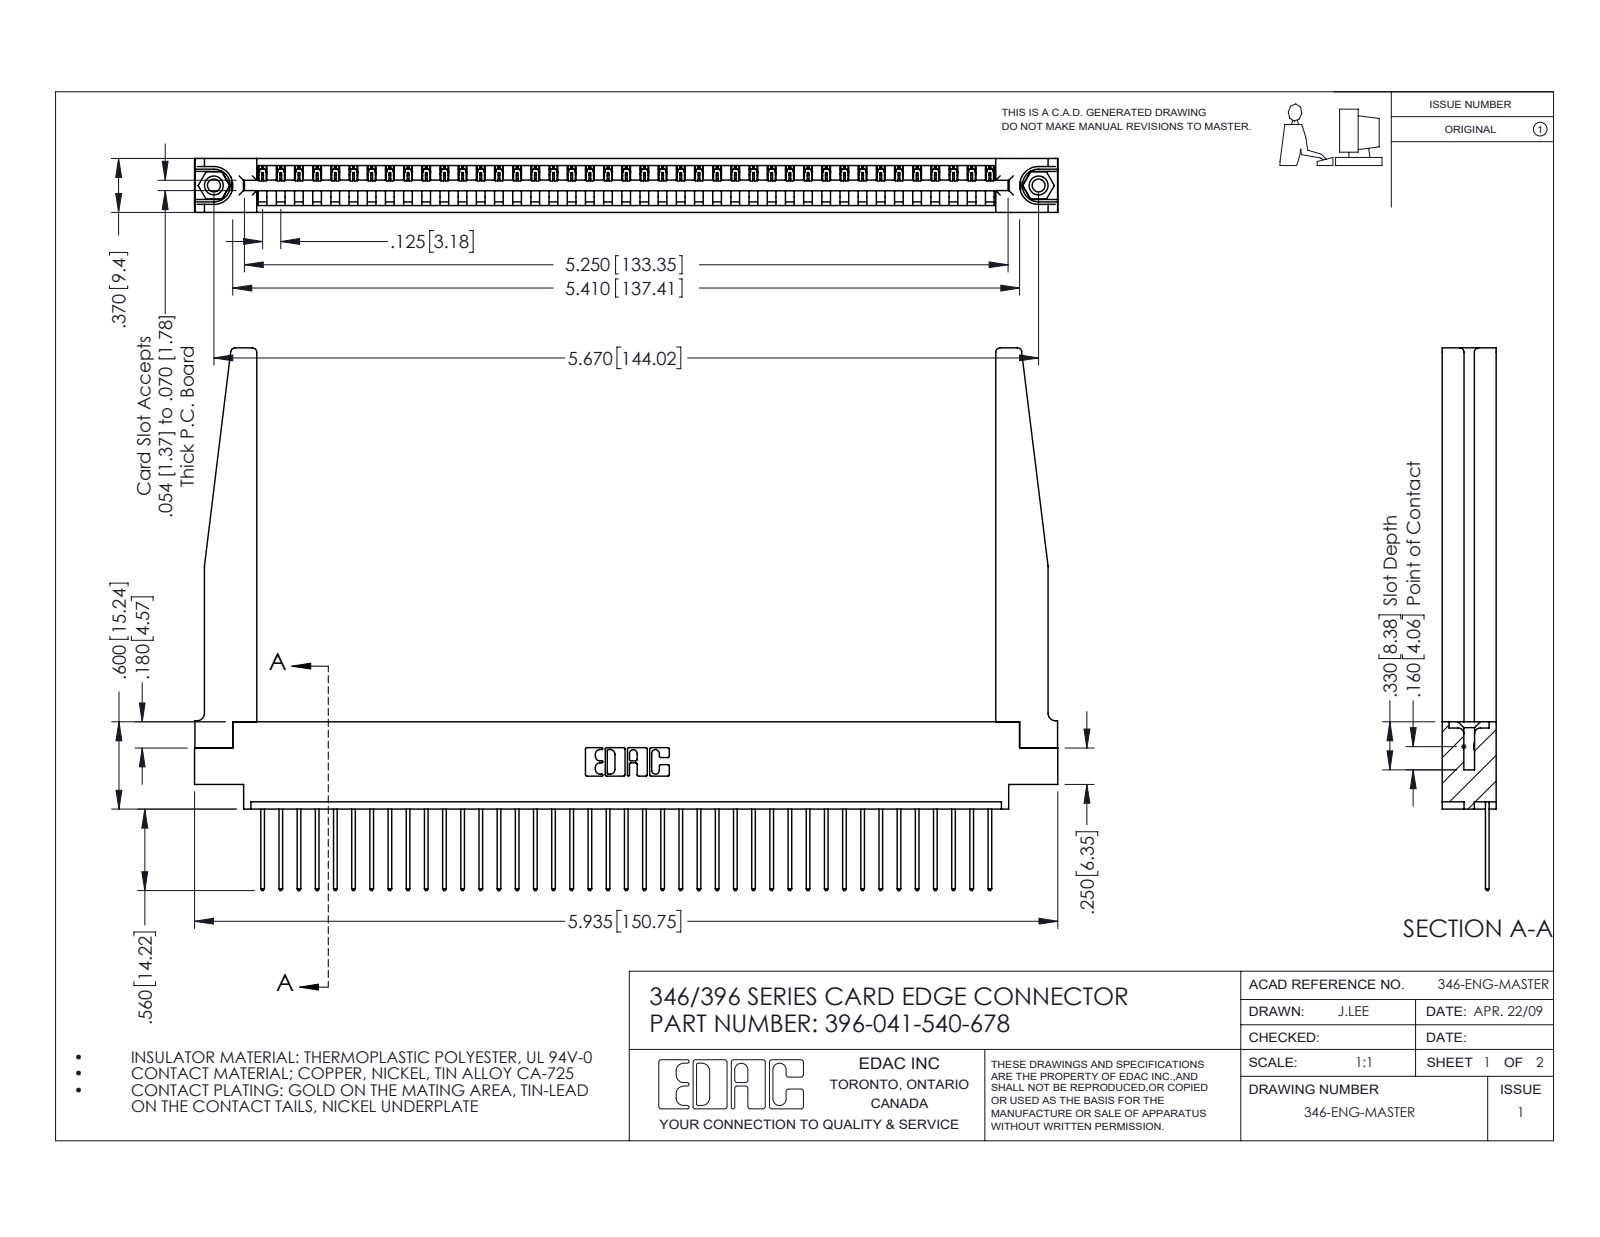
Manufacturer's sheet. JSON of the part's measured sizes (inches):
{"part_name": "346 Part_0.170 Offset - 0.156 Dia-TH; 345-250-001_345-250-001-102; 396-041-540-678; 345-292-001_345-293-140 (+1 more)", "step_written_by": "SolidWorks 2016 (CONFIG_CONTROL_DESIGN)", "units": "inches", "bodies": {"solids": 46, "faces": 2738, "planar": 1862, "cylindrical": 824, "other": 52}, "overall_size": [5.935, 3.73, 0.37], "volume_in3": 1.296, "surface_area_in2": 38.75, "round_holes": [[0.089, 2], [0.125, 2], [0.156, 2], [0.064, 1]], "round_bosses_or_shafts": [[0.155, 2]], "partial_cylinders_radius": [[0.006, 82], [0.01, 82], [0.01, 22], [0.03, 8], [0.007, 6], [0.031, 6], [0.026, 3], [0.031, 2]], "face_to_face_distances": [0.37, 0.048, 0.322, 0.072, 0.148, 0.25, 0.15, 0.298, 0.025, 0.222], "hole_center_spacings": [0.246, 5.461, 5.67]}
